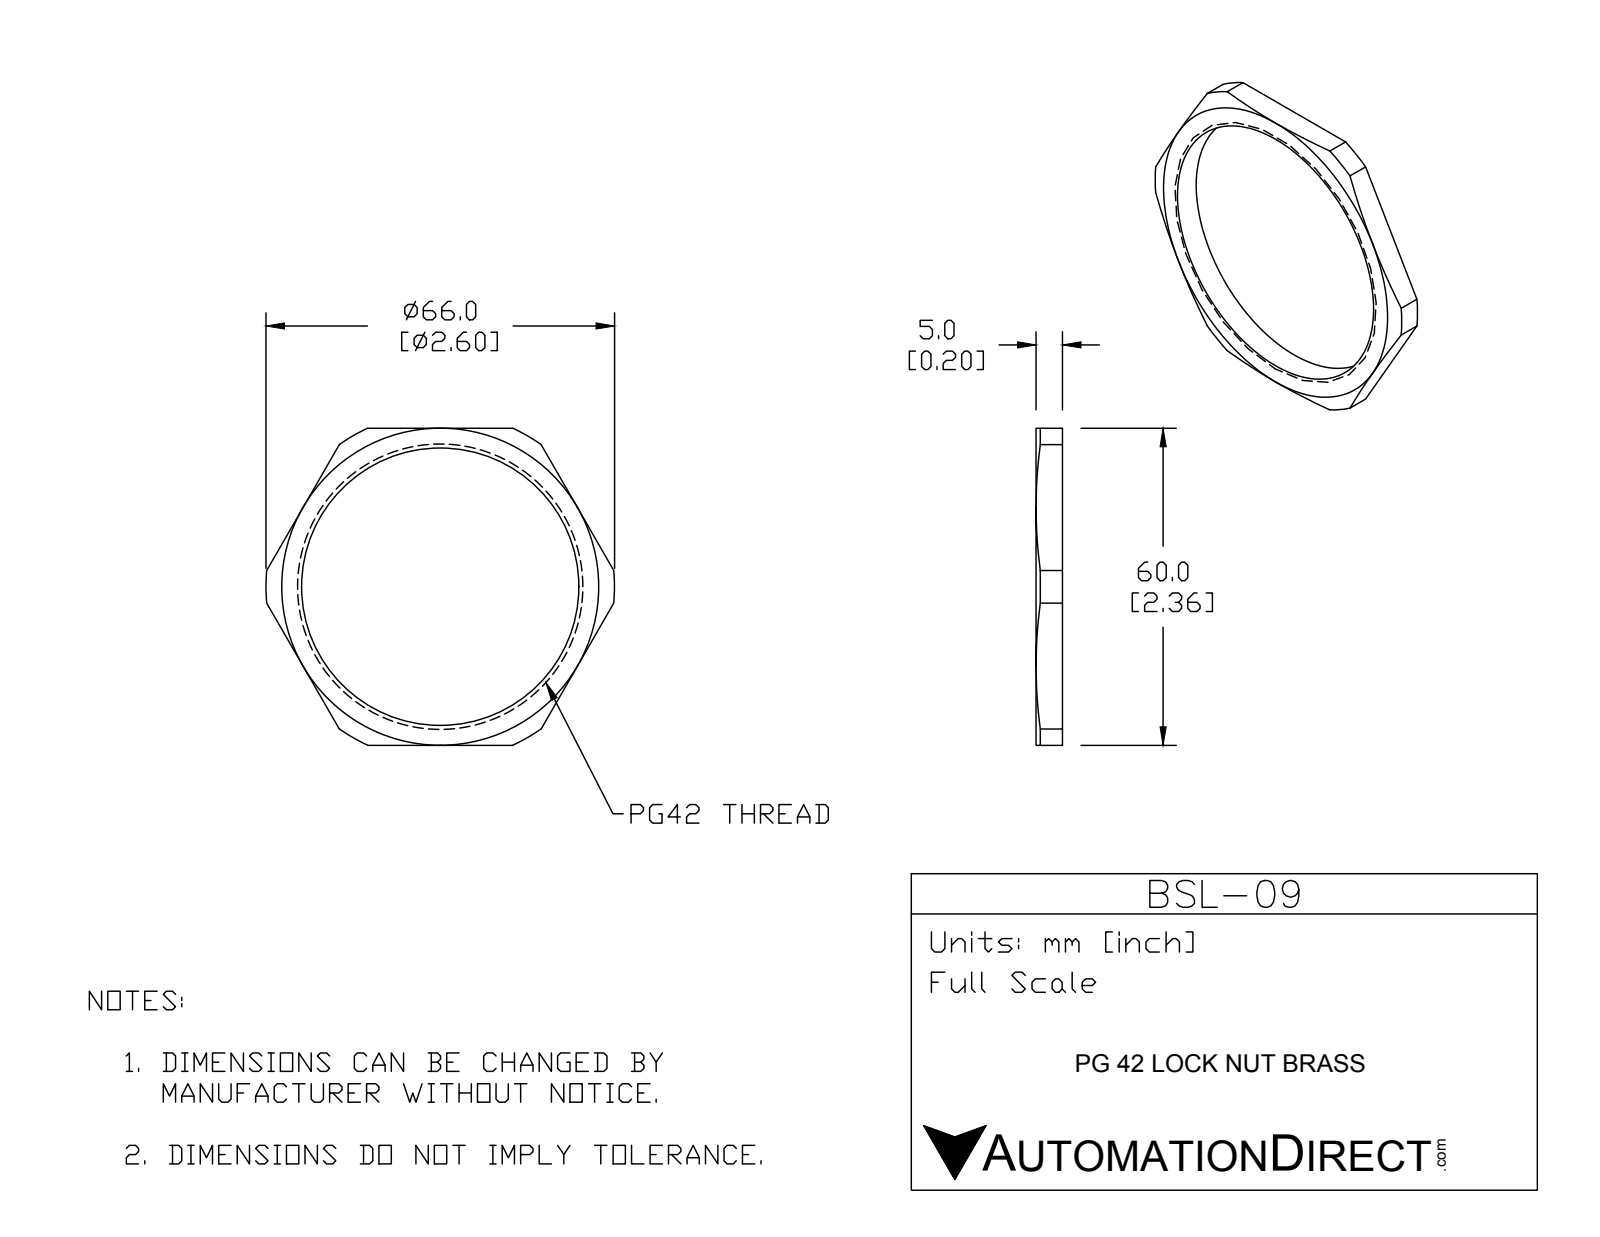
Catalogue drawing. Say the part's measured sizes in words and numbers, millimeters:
The part is named "BSL-09". Its 3-D file was written by "SolidWorks 2015 (CONFIG_CONTROL_DESIGN)". It is 1 solid with 23 faces: 8 planar, 9 cylindrical and 6 other. Overall it measures 66 by 60 by 5 millimeters. Its volume is 4 536 cubic millimeters and its surface area 3 616 square millimeters. Round holes: 1 of diameter 52.5. Partial cylindrical surfaces (rounded edges, fillets, slot ends): 1 of radius 33. The main face-to-face distances are 5, 60.
